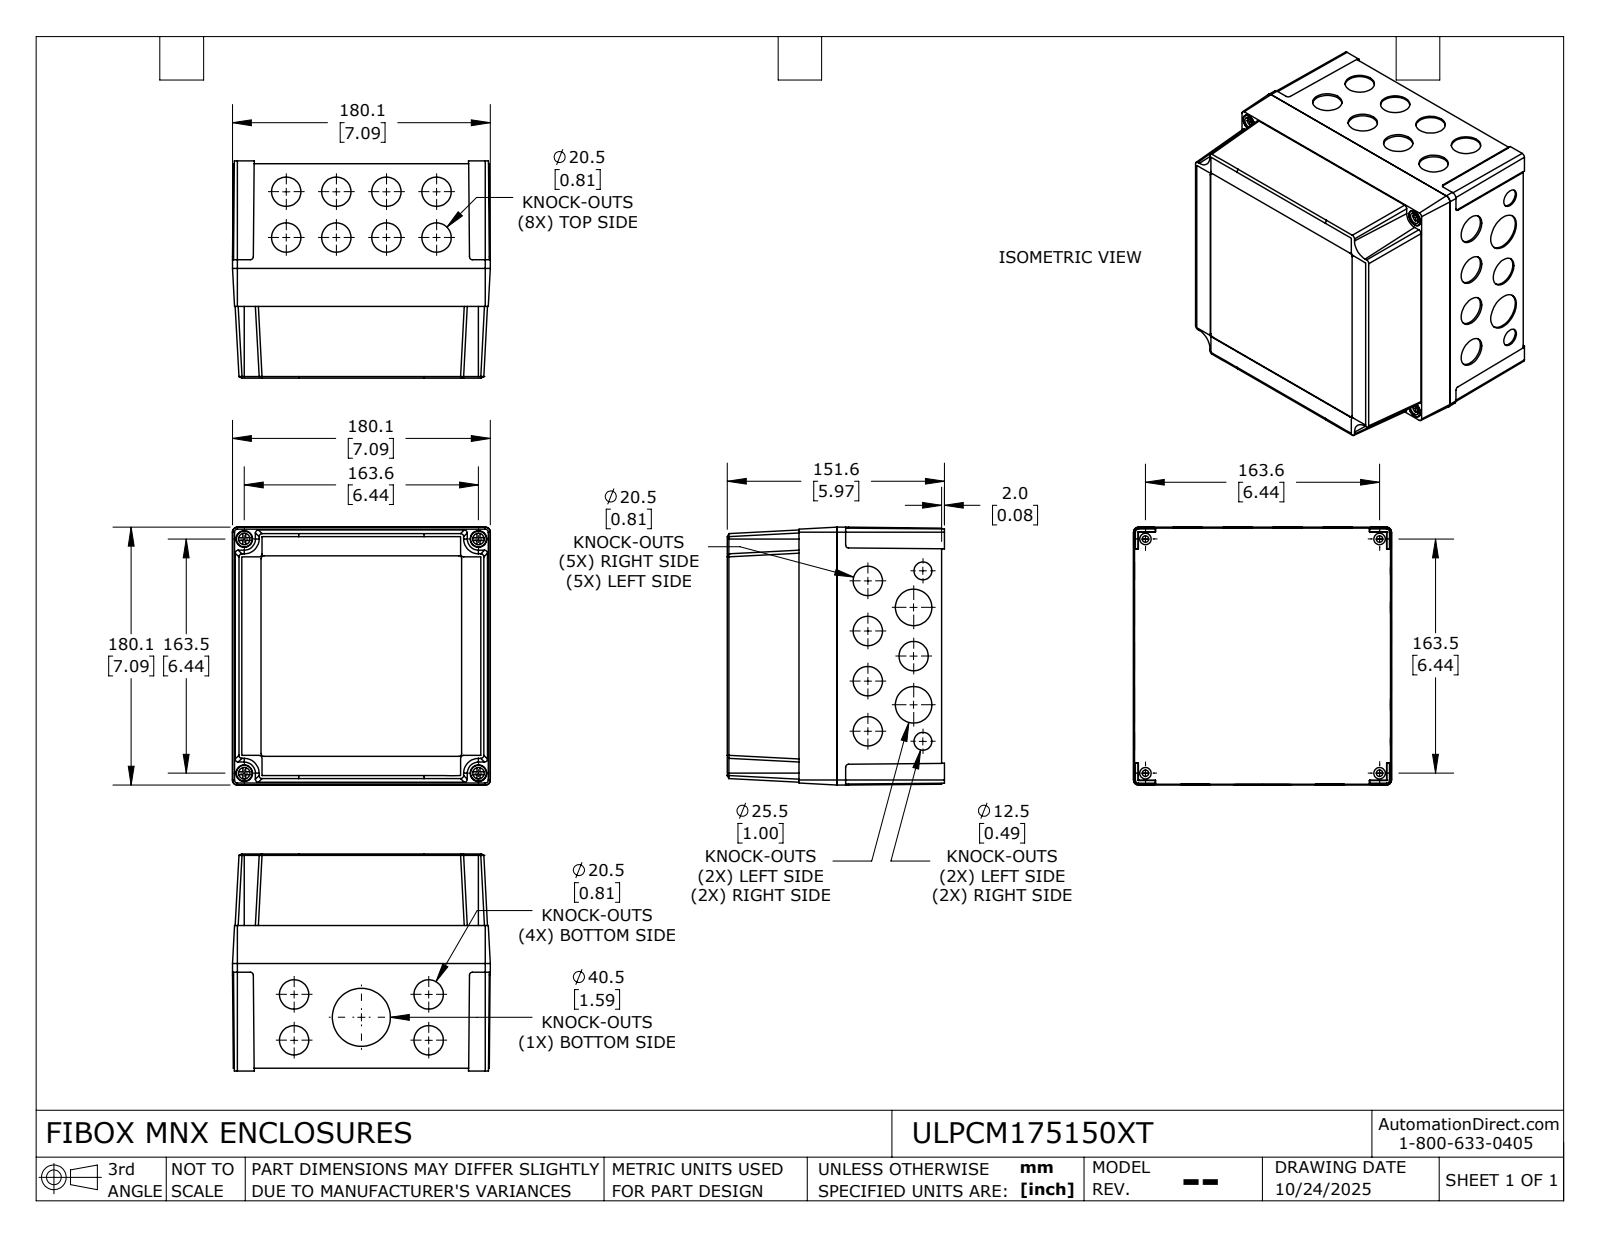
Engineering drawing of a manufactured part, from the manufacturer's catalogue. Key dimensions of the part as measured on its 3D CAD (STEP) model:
Part name (STEP PRODUCT): ULPCM175150XG_Default
STEP written by: SolidWorks 2024 (CONFIG_CONTROL_DESIGN)
Units: millimetres
Bodies: 12 solids, 544 faces (358 planar, 136 cylindrical, 50 other)
Overall size (bounding box): 180.1 × 180.1 × 151.6
Volume: 511 430 mm³ · Surface area: 348 027 mm²
Round holes (diameter × count): ⌀20.5 ×17, ⌀3.2 ×12, ⌀4 ×12, ⌀8 ×8, ⌀4.5 ×4, ⌀11.6 ×4, ⌀12.5 ×2, ⌀25.5 ×2, ⌀40.5 ×1
Round bosses / shafts (diameter × count): ⌀8 ×12, ⌀2.5 ×8, ⌀11 ×4, ⌀7.2 ×4
Partial cylindrical surfaces — rounded edges, fillets, slot ends (radius × count): R2 ×8, R2.1 ×8, R5 ×4
Main face-to-face distances: 4.2, 3, 1.4, 146.7, 143.7, 149.1, 146.1, 2.4, 1.96, 0.56
Hole centre spacings: 163.5, 35, 33.85, 50, 72.8, 82.59, 121.66, 132.27
